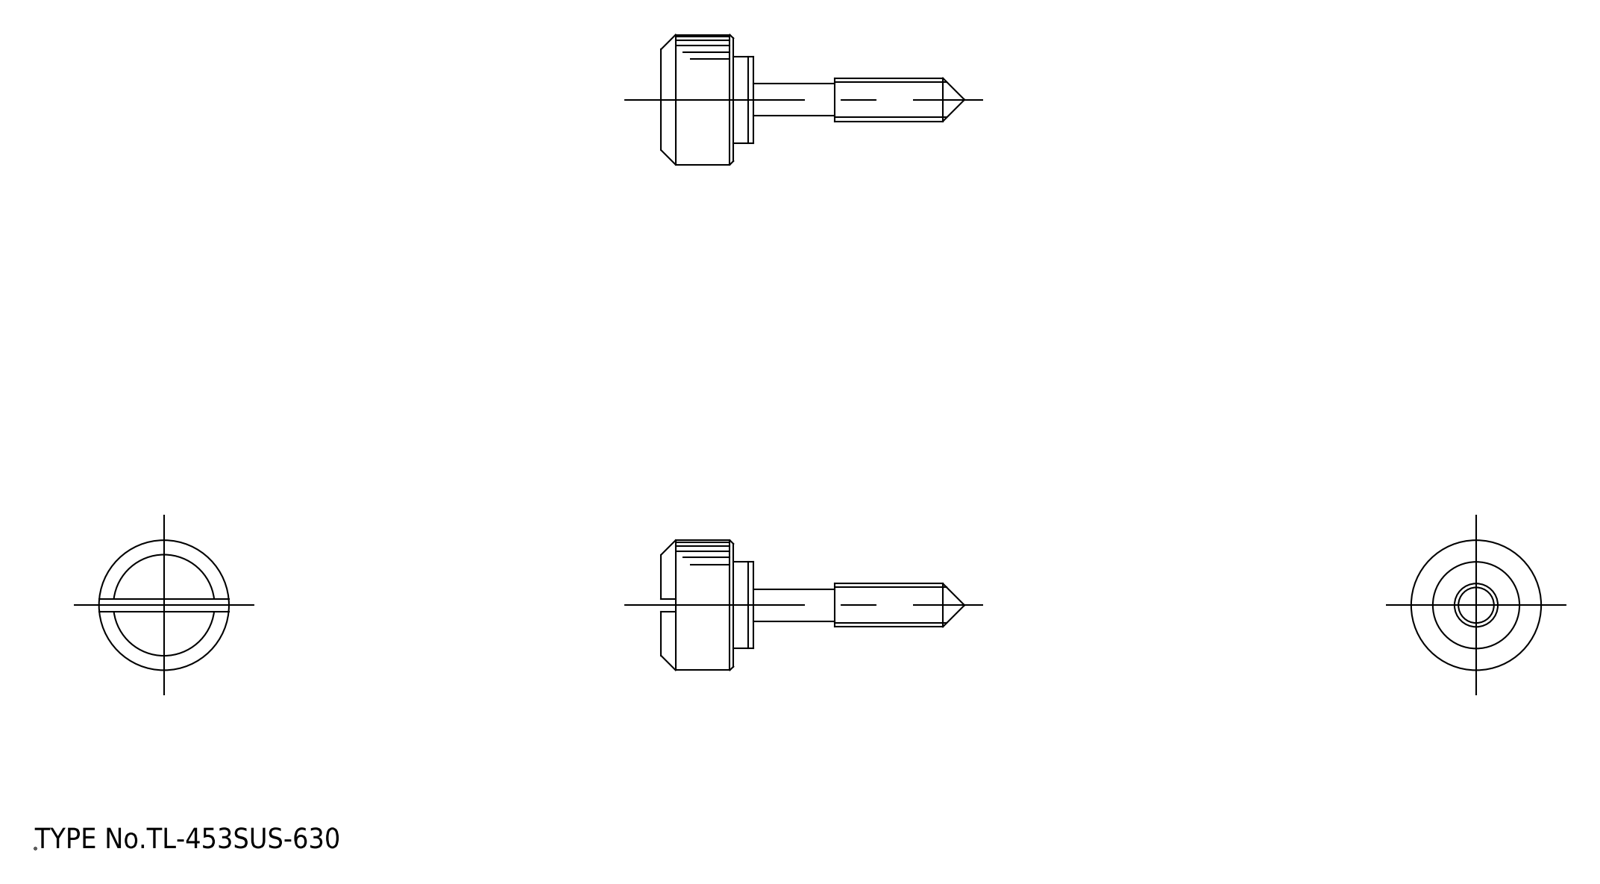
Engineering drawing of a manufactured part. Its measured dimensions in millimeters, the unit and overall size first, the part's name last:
Units: millimetres
Overall size (bounding box): 42 × 18 × 18
Round bosses / shafts (diameter × count): ⌀18 ×1, ⌀12 ×1, ⌀6 ×1, ⌀4.5 ×1
Partial cylindrical surfaces — rounded edges, fillets, slot ends (radius × count): R1 ×4, R2.3 ×1
Main face-to-face distances: 2, 10, 12, 12.8, 2.8, 0.8, 8, 10.8, 1.8, 24
Volume: 3 314 mm³ · Surface area: 1 830 mm²
Bodies: 2 solids, 42 faces (18 planar, 18 cylindrical, 6 other)
Part name (STEP PRODUCT): washer; knob
STEP written by: spGate 19.8.4 (****-****-****-****) (AUTOMOTIVE_DESIGN)
